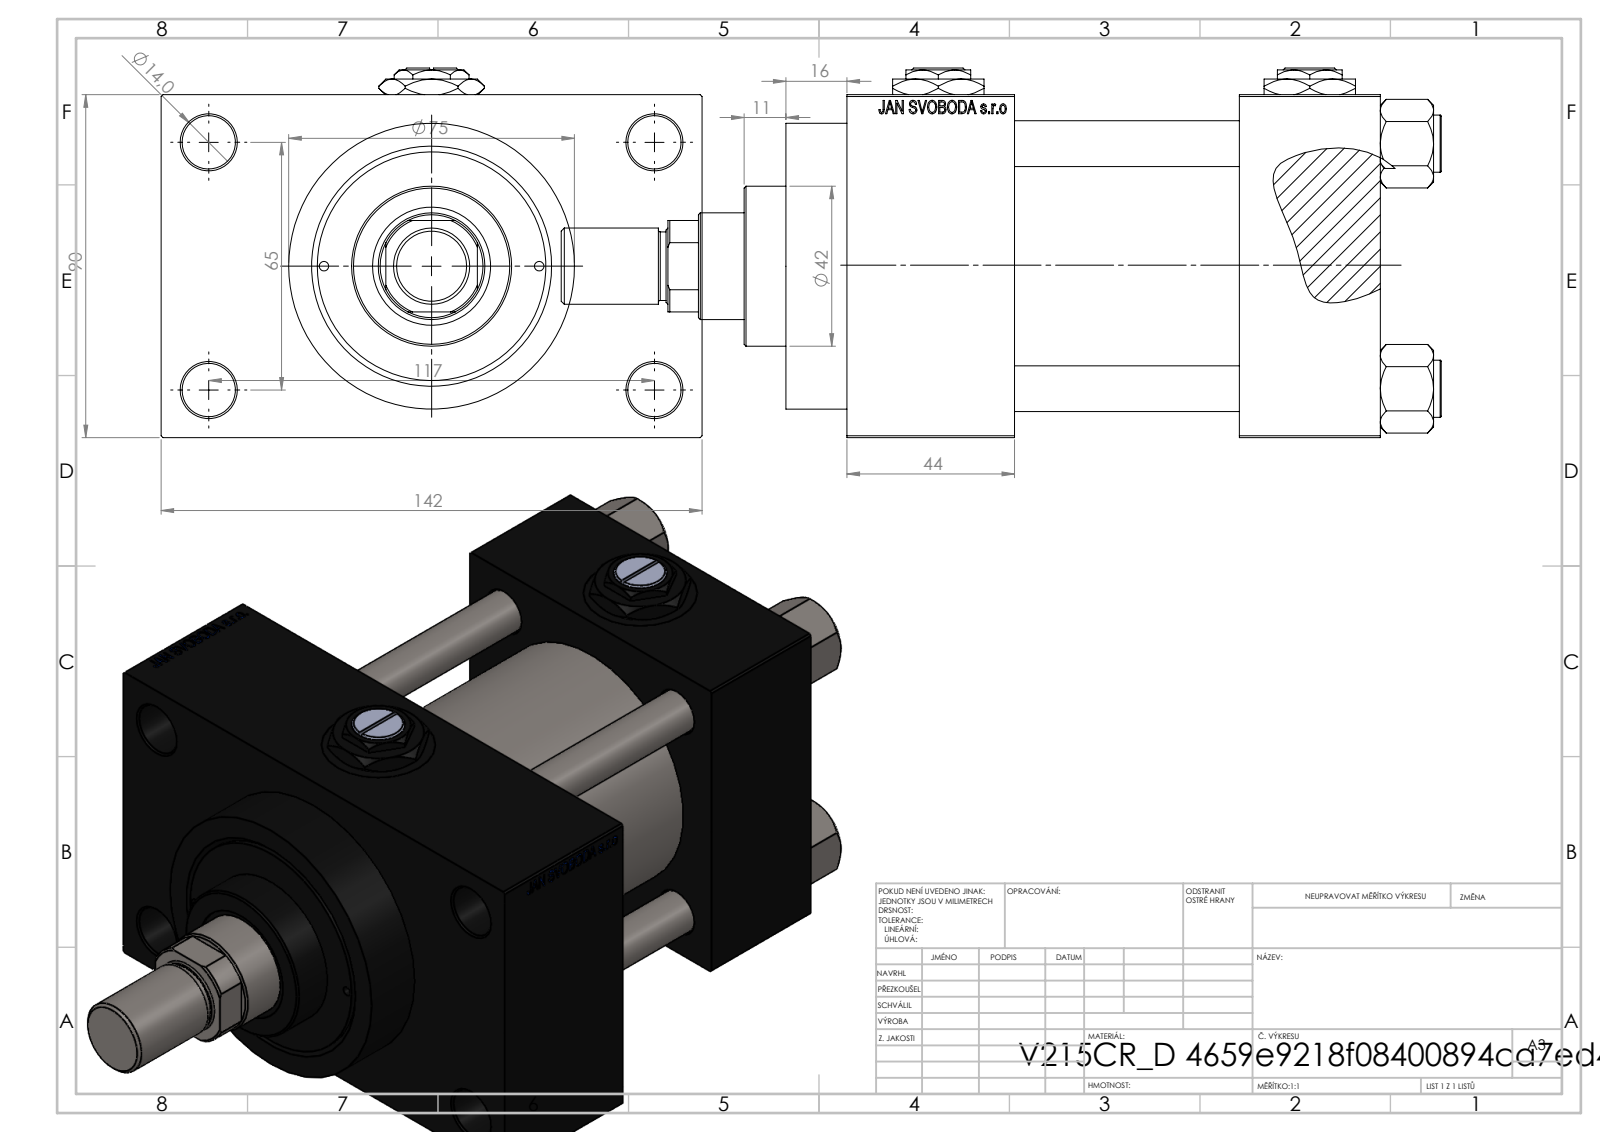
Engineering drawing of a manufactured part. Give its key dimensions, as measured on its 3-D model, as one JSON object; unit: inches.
{"part_name": "V215_VC_A; V215CR_D_TYCINKA; V215CR_D_Body; NUT_M5_D (+3 more)", "step_written_by": "SolidWorks 2019 (CONFIG_CONTROL_DESIGN)", "units": "inches", "bodies": {"solids": 14, "faces": 1226, "planar": 551, "cylindrical": 107, "other": 568}, "overall_size": [9.094, 5.591, 3.819], "volume_in3": 67.07, "surface_area_in2": 321.3, "round_holes": [[0.472, 4], [0.551, 4], [0.825, 4], [1.181, 4], [0.276, 3], [0.098, 2], [0.728, 1], [1.102, 1], [1.22, 1], [1.969, 1], [2.362, 1], [2.48, 1]], "round_bosses_or_shafts": [[0.591, 4], [2.953, 1], [2.717, 1], [1.654, 1], [0.787, 1], [0.709, 1]], "partial_cylinders_radius": [[0.531, 1]], "face_to_face_distances": [3.543, 2.323, 1.457, 3.78, 5.512, 4.055, 1.732, 1.024, 4.567, 5.591], "hole_center_spacings": [1.037, 1.275, 1.748, 1.79, 2.531, 2.635, 2.694, 2.748]}
